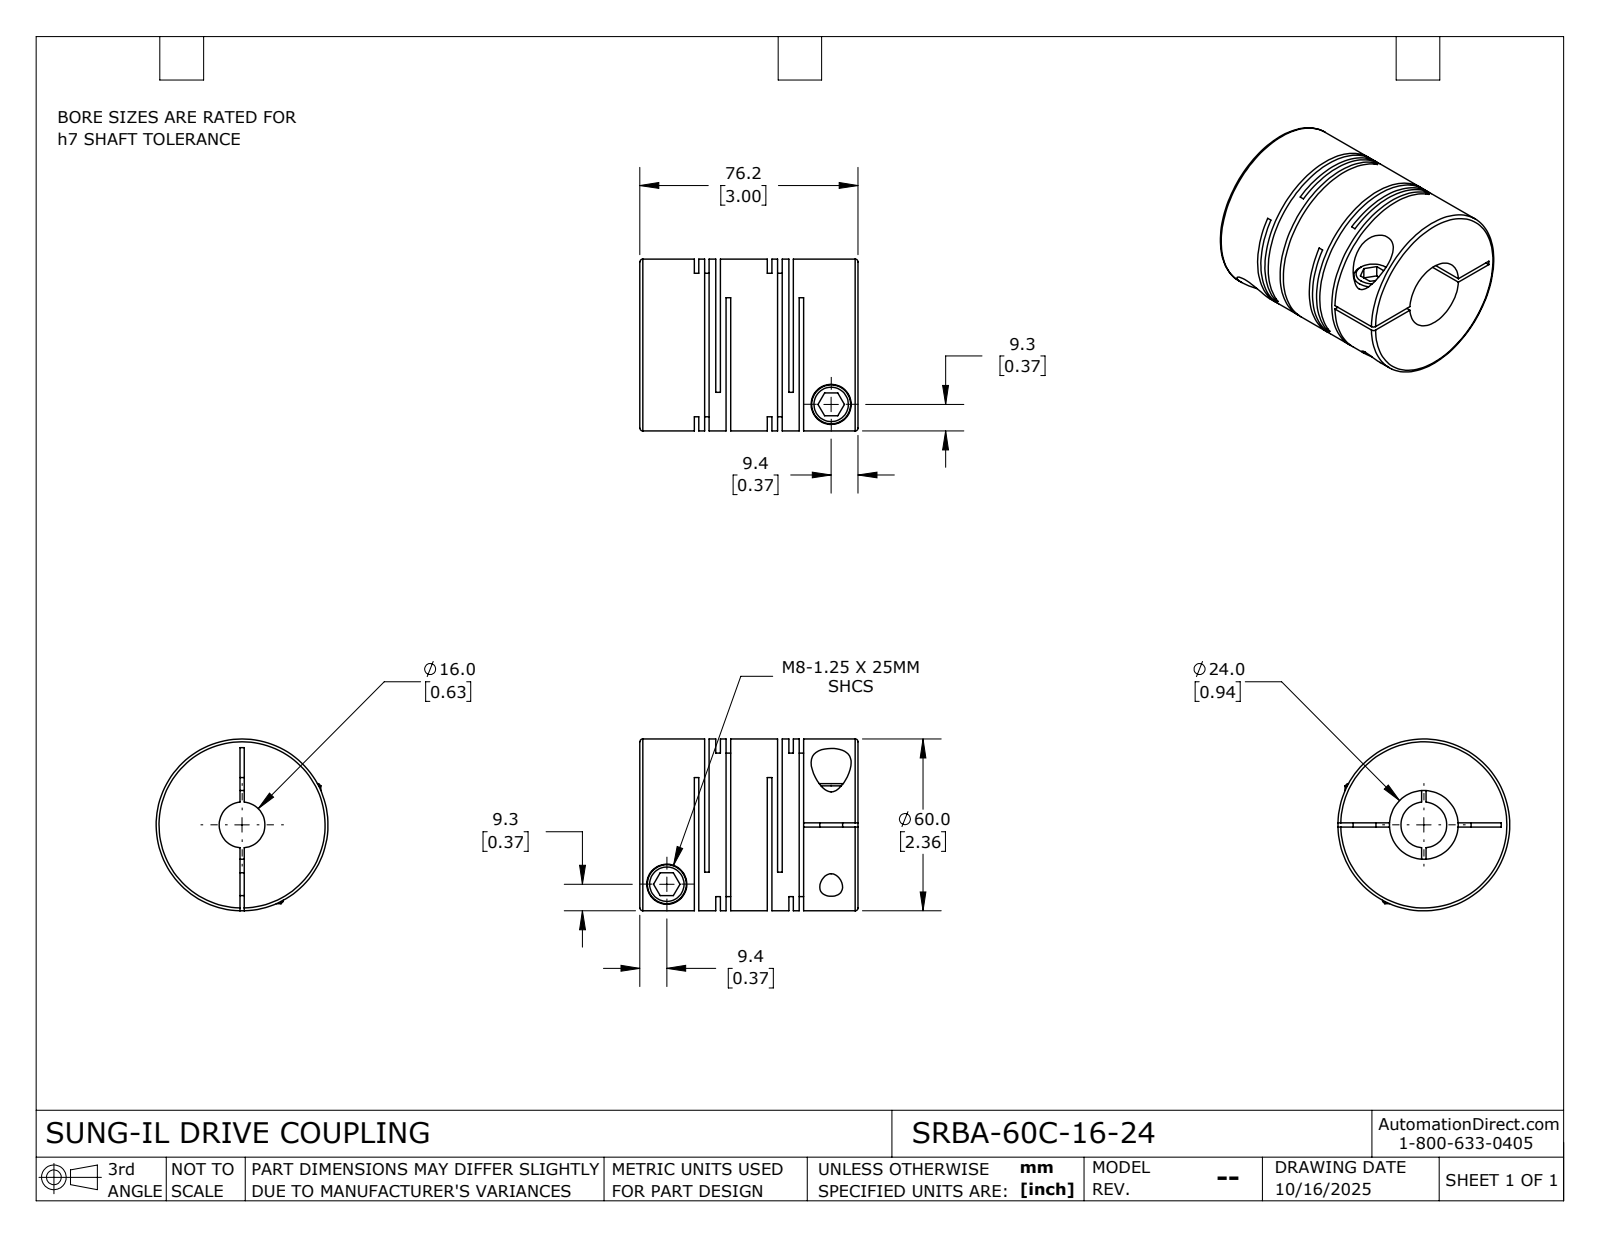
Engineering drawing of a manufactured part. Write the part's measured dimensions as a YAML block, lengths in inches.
part_name: "SRBA-60C-16-24"
step_written_by: "SolidWorks 2024 (CONFIG_CONTROL_DESIGN)"
units: inches
bodies: {solids: 1, faces: 115, planar: 60, cylindrical: 42, other: 13}
overall_size: [3, 2.362, 2.362]
volume: 9.537
surface_area: 89.06
round_holes:
  - {diameter: 0.315, count: 2}
  - {diameter: 0.551, count: 2}
  - {diameter: 0.63, count: 1}
  - {diameter: 0.945, count: 1}
round_bosses_or_shafts:
  - {diameter: 0.535, count: 2}
  - {diameter: 2.362, count: 1}
face_to_face_distances: [0.063, 0.142, 0.295, 1.004, 1.299, 1.067, 0.079, 0.232, 0.941, 0.154]
